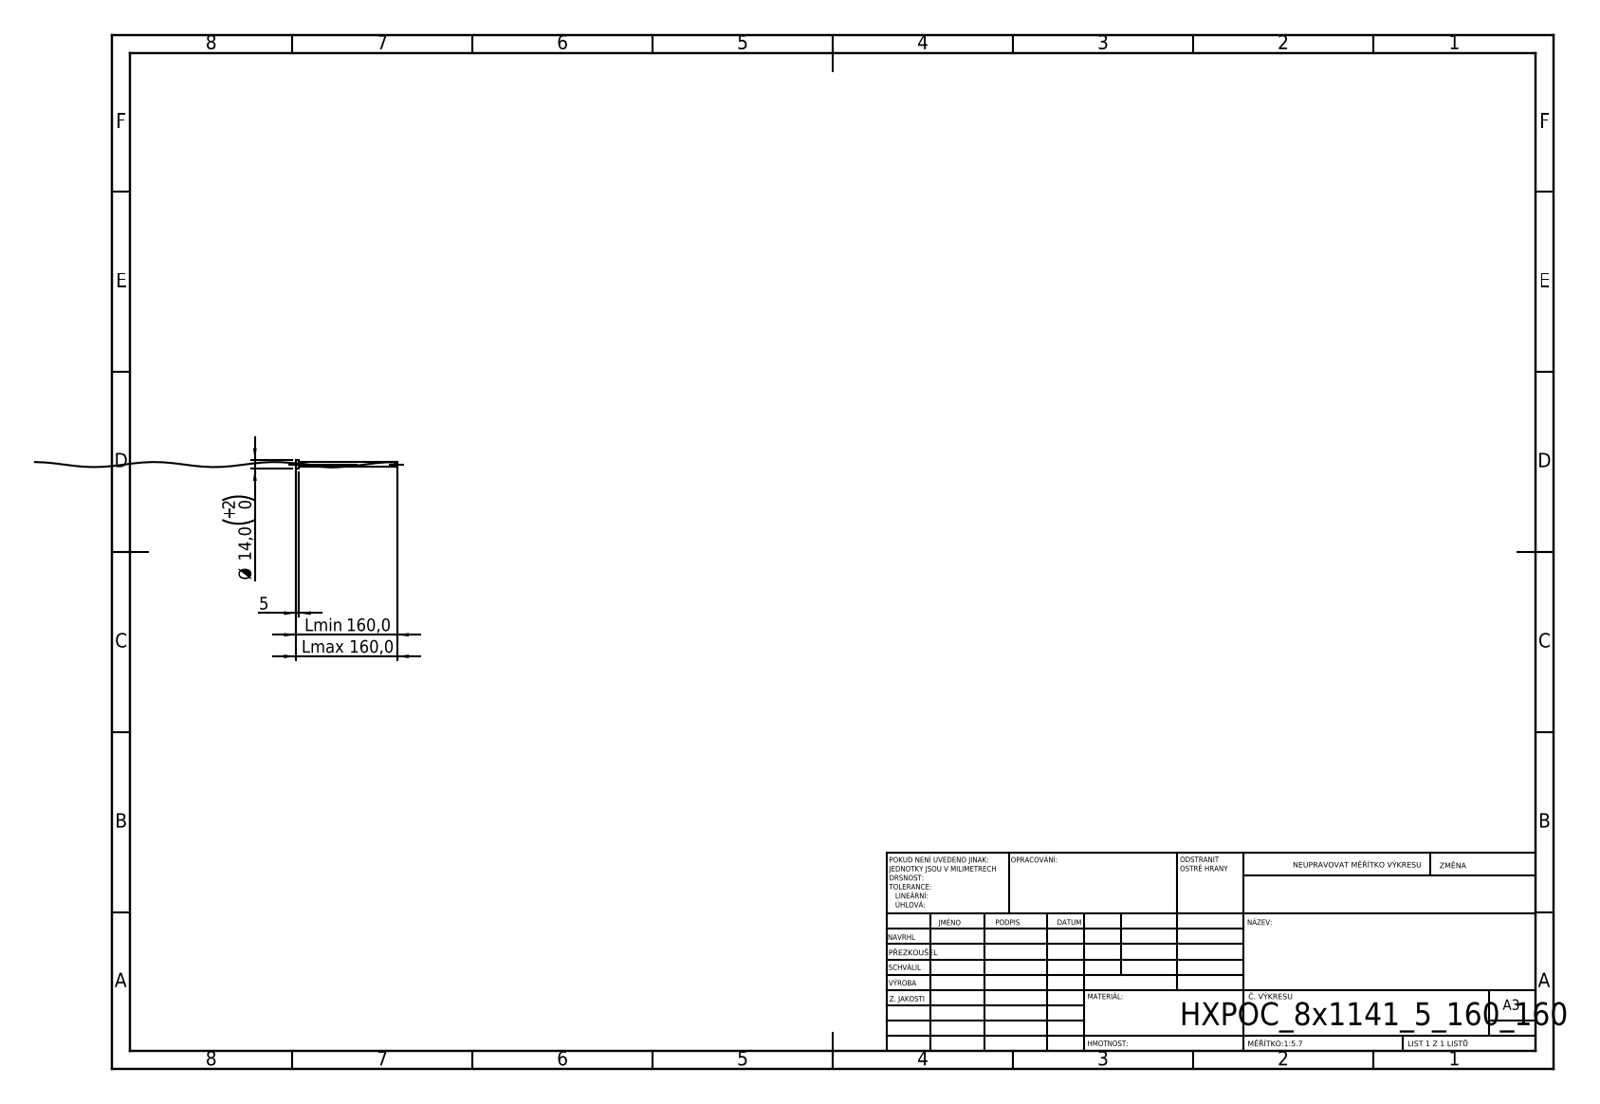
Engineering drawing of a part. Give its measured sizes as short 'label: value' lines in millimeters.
written by: SolidWorks 2019 (CONFIG_CONTROL_DESIGN)
unit: mm
bodies: 1 solid, 16 faces (5 planar, 9 cylindrical, 2 other)
size: 160 × 14 × 14
volume: 8 381 mm³; area: 4 585 mm²
bosses: 1× ⌀14, 1× ⌀8, 1× ⌀6.4
face distances: 5, 160, 155, 158.11, 153.11, 1.89, 156.51, 151.51, 1.6, 3.49
